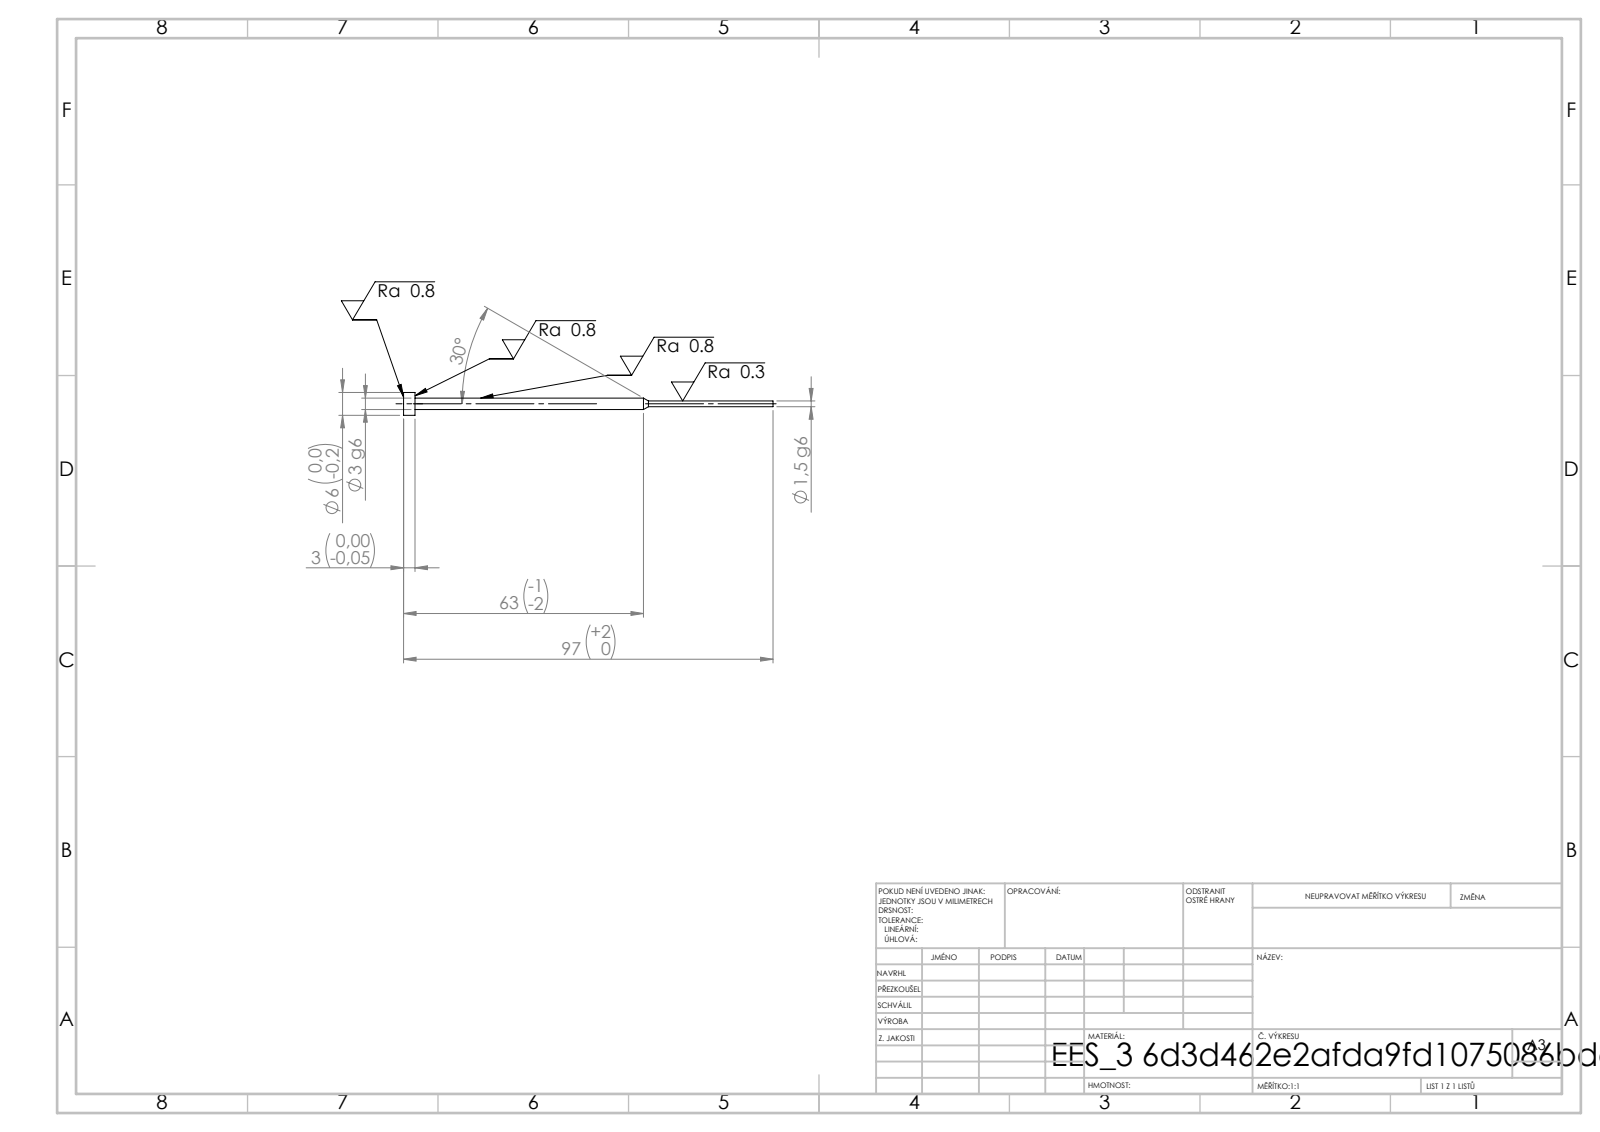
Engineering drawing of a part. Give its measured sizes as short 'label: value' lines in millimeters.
written by: SolidWorks 2019 (CONFIG_CONTROL_DESIGN)
unit: mm
bodies: 1 solid, 11 faces (3 planar, 6 cylindrical, 2 other)
size: 97 × 6 × 6
volume: 572 mm³; area: 838 mm²
bosses: 1× ⌀6, 1× ⌀3, 1× ⌀1.5
face distances: 3, 94, 97
